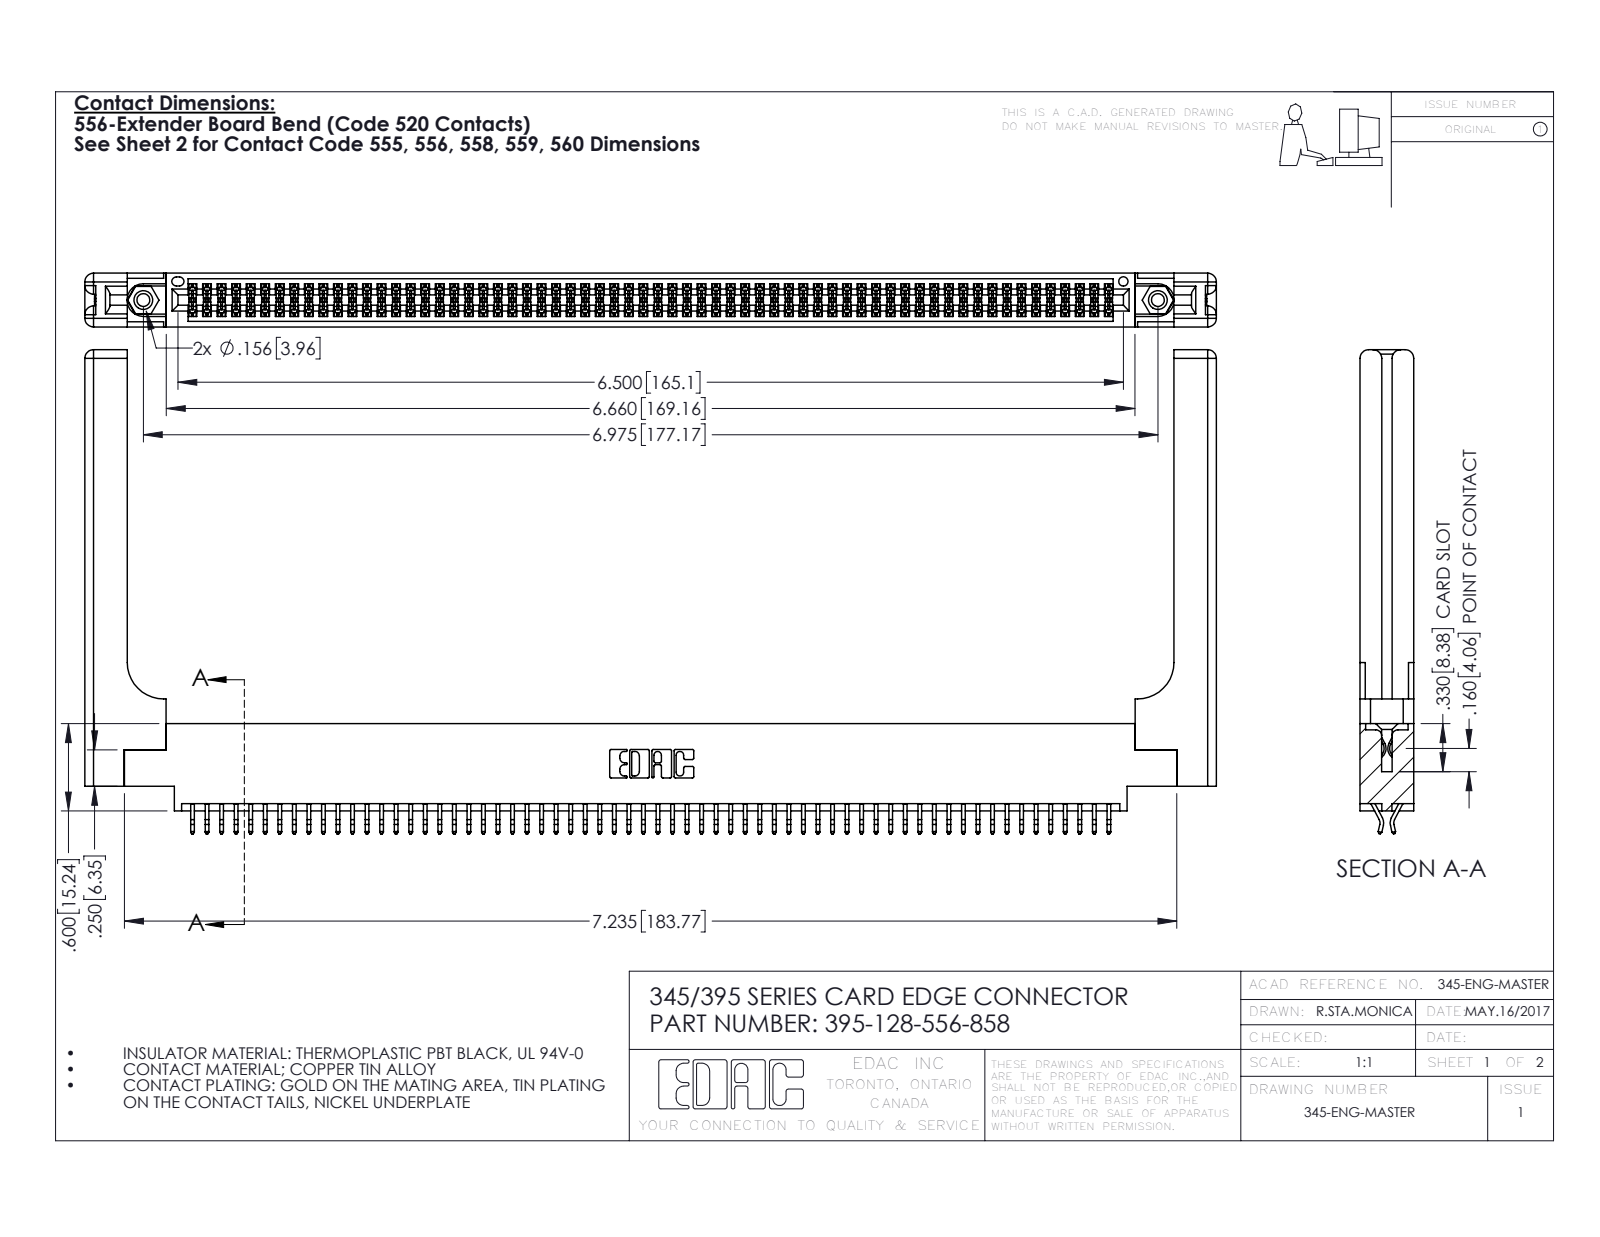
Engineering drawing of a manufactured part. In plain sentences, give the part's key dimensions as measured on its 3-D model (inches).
The part is named "345-250-001_345-250-001-102; 395-128-556-858; 345-220-058_345-220-058; 345-292-001_556 Tail (+1 more)". Its 3-D file was written by "SolidWorks 2016 (CONFIG_CONTROL_DESIGN)". It is 133 solids with 7554 faces: 4968 planar, 2526 cylindrical and 60 other. Overall it measures 7.779 by 3.327 by 0.37 inches. Its volume is 1.694 cubic inches and its surface area 52.72 square inches. Round holes: 2 of diameter 0.089, 2 of diameter 0.125, 2 of diameter 0.156, 1 of diameter 0.064. Round bosses or shafts: 2 of diameter 0.155. Partial cylindrical surfaces (rounded edges, fillets, slot ends): 192 of radius 0.006, 22 of radius 0.01, 16 of radius 0.06, 6 of radius 0.007, 6 of radius 0.031, 3 of radius 0.026, 2 of radius 0.01, 2 of radius 0.014. The main face-to-face distances are 0.072, 0.298, 0.37, 0.025, 0.098, 0.272, 0.2, 0.225, 0.175, 0.148. The hole center spacings are 0.27, 6.739, 6.975.
